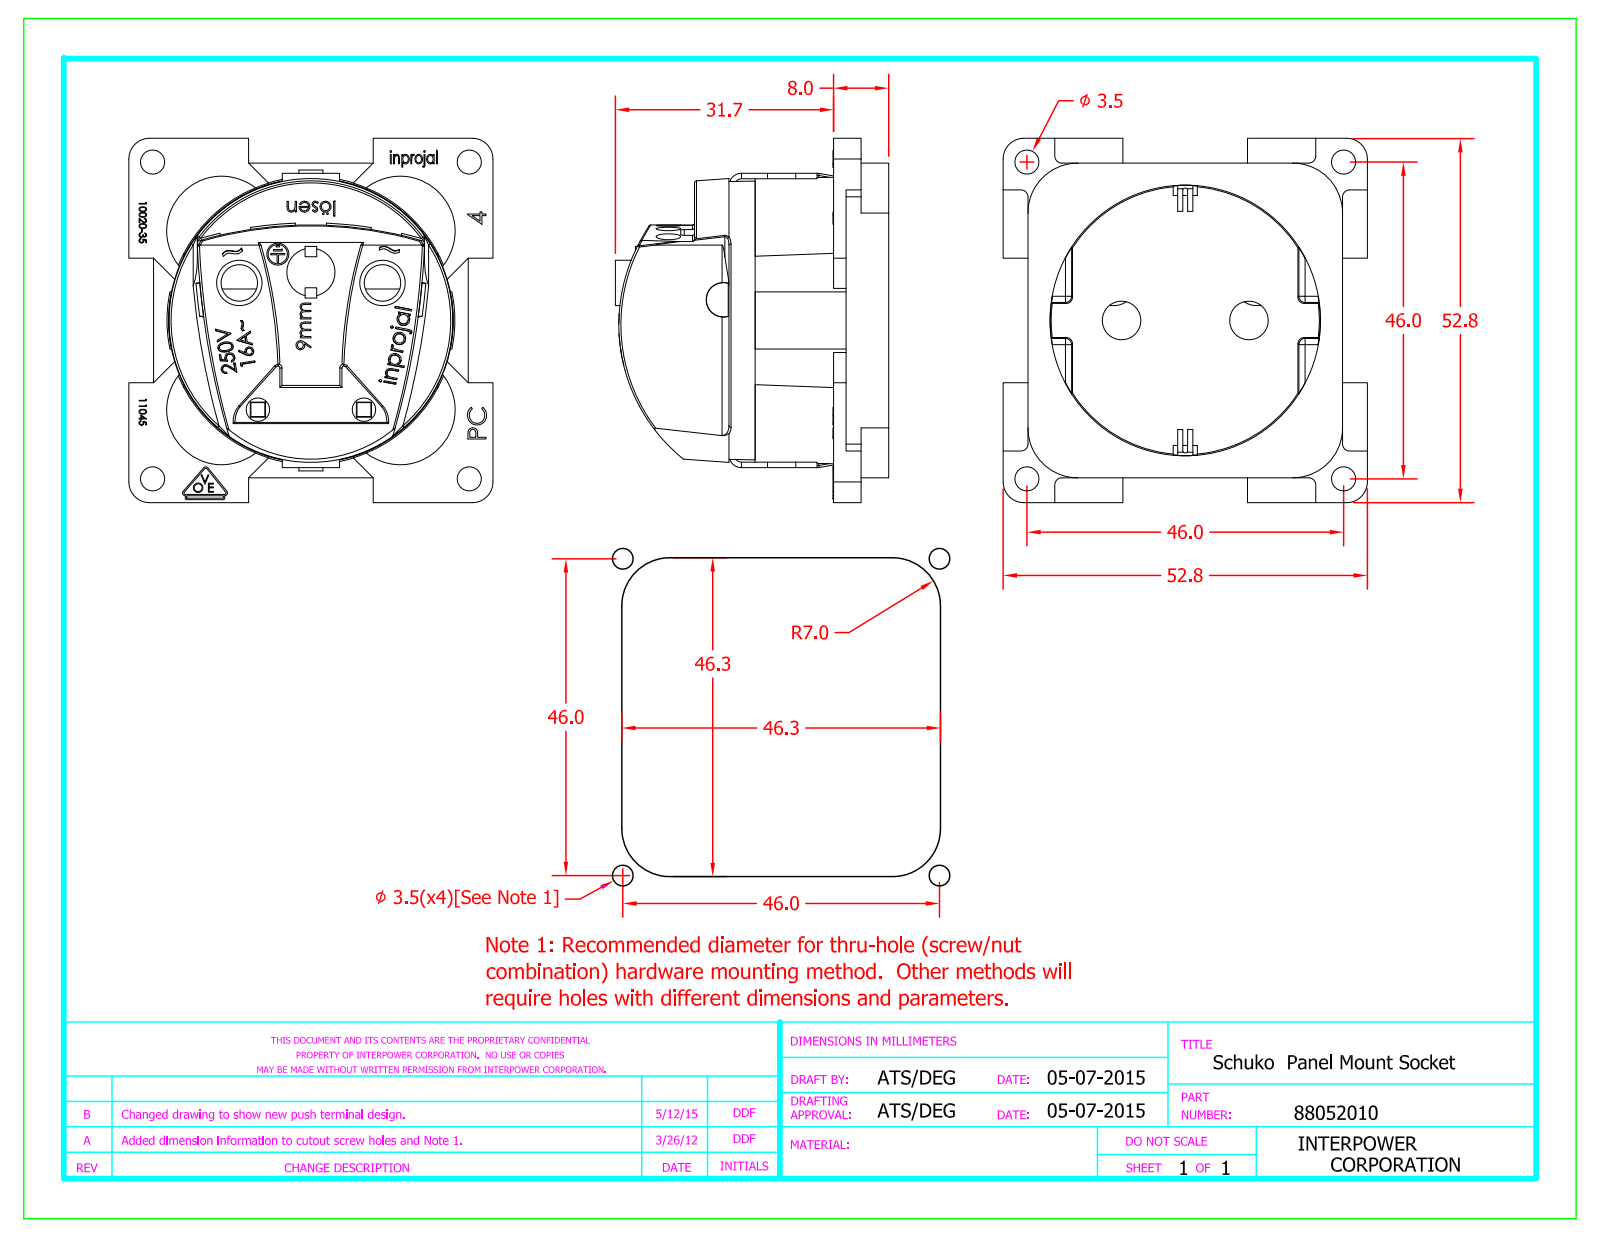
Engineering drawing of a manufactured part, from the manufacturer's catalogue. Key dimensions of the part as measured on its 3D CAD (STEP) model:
Part name (STEP PRODUCT): 88052010
STEP written by: SolidWorks 2014 (CONFIG_CONTROL_DESIGN)
Units: inches
Bodies: 8 solids, 1162 faces (485 planar, 186 cylindrical, 491 other)
Overall size (bounding box): 2.083 × 2.083 × 1.563
Volume: 1.751 in³ · Surface area: 29.6 in²
Round holes (diameter × count): ⌀0.138 ×4, ⌀0.01 ×2, ⌀0.134 ×2, ⌀0.209 ×2, ⌀0.22 ×2, ⌀0.126 ×1
Round bosses / shafts (diameter × count): ⌀0.26 ×2, ⌀0.276 ×1, ⌀0.11 ×1
Partial cylindrical surfaces — rounded edges, fillets, slot ends (radius × count): R0.012 ×16, R0.035 ×8, R0.039 ×8, R0.118 ×6, R0.008 ×5, R0.04 ×4, R0.071 ×4, R0.285 ×4
Main face-to-face distances: 0.059, 0.315, 0.764, 0.705, 0.39, 0.449, 0.52, 0.071, 1.11, 0.461
Hole centre spacings: 1.055, 1.559, 1.811, 1.016, 0.219, 0.513, 0.721, 0.732
